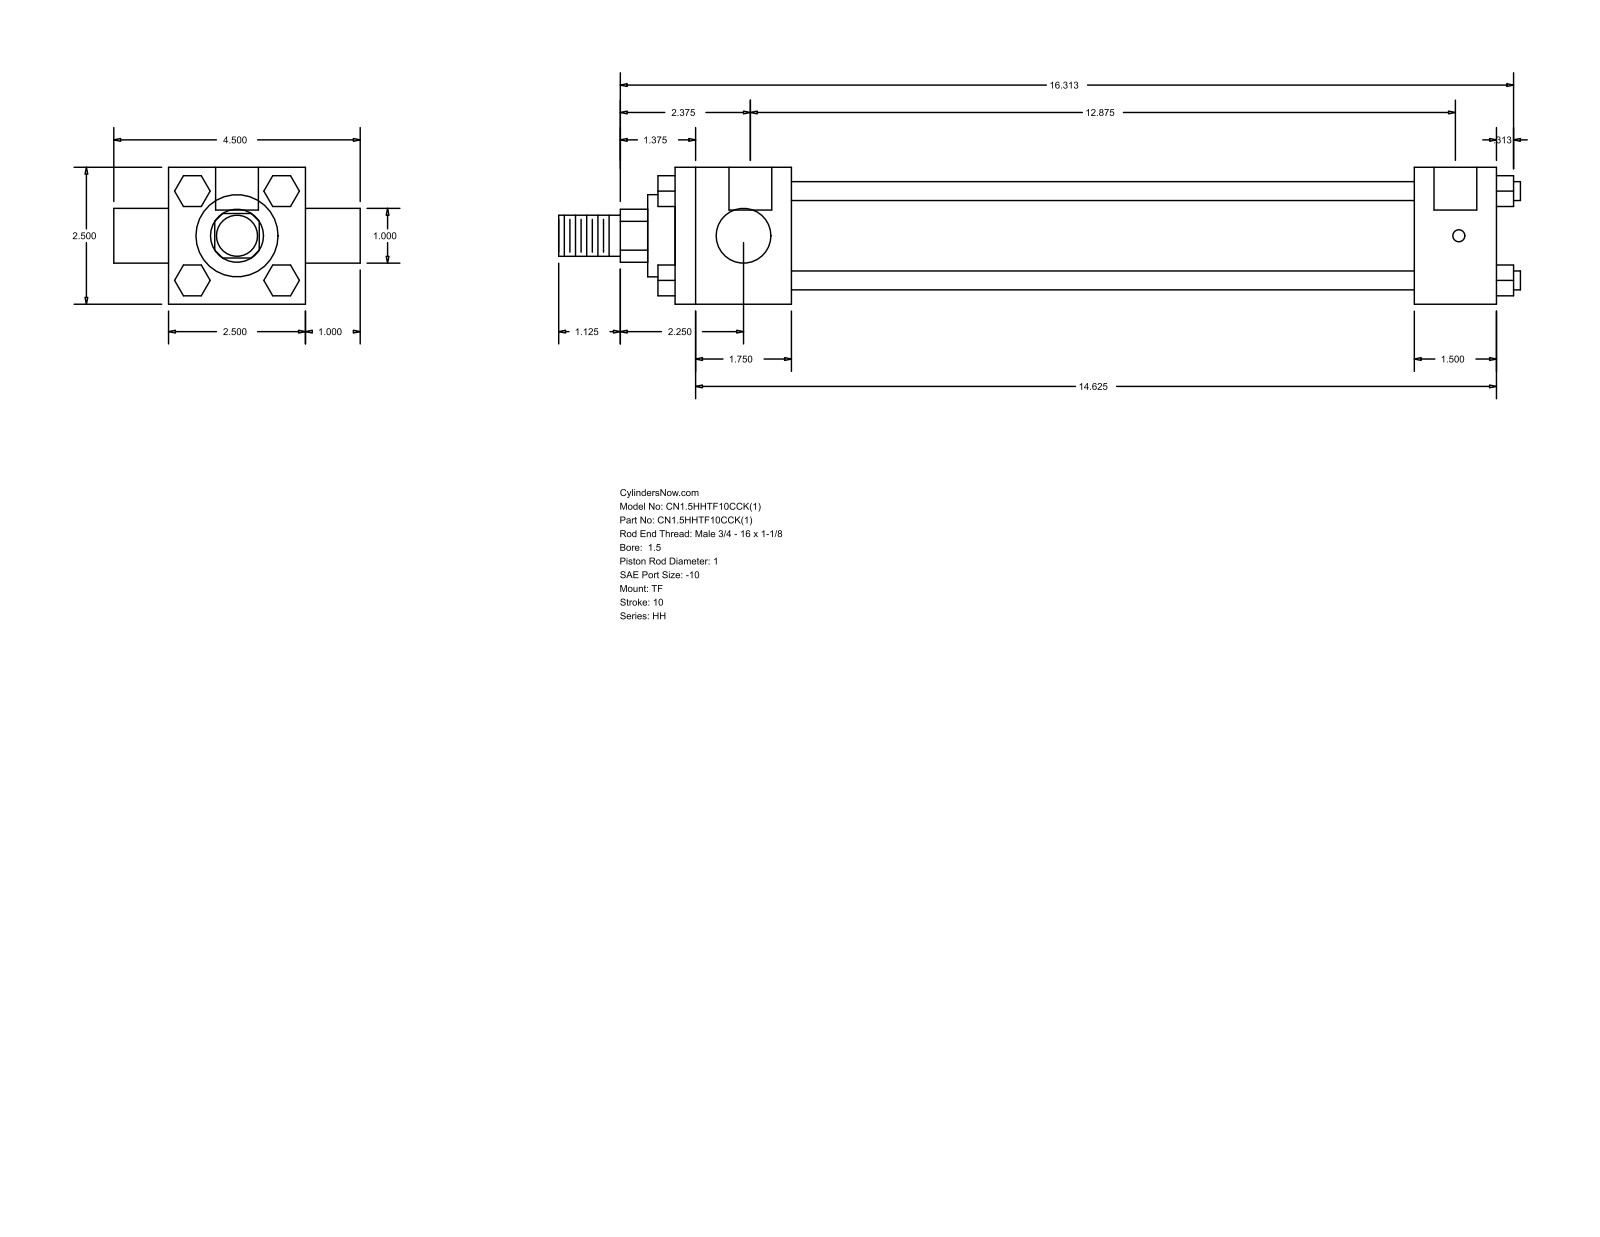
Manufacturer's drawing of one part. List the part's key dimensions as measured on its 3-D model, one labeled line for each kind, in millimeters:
Part name (STEP PRODUCT): HH_TF__0150_1
STEP written by: GSSL Pune (CONFIG_CONTROL_DESIGN)
Units: millimetres
Bodies: 0 solids, 120 faces (92 planar, 28 cylindrical, 0 other)
Overall size (bounding box): 446.09 × 114.3 × 63.5
Round holes (diameter × count): ⌀5.56 ×3, ⌀19.84 ×2
Round bosses / shafts (diameter × count): ⌀8.76 ×4, ⌀25.4 ×2, ⌀44.45 ×1, ⌀38.1 ×1, ⌀19.05 ×1
Partial cylindrical surfaces — rounded edges, fillets, slot ends (radius × count): R12.29 ×1
Main face-to-face distances: 63.5, 38.1, 327.02, 288.92, 53.98, 342.9, 381, 25.4, 20.7, 14.29
Hole centre spacings: 1.59, 328.61, 327.02, 330.2
